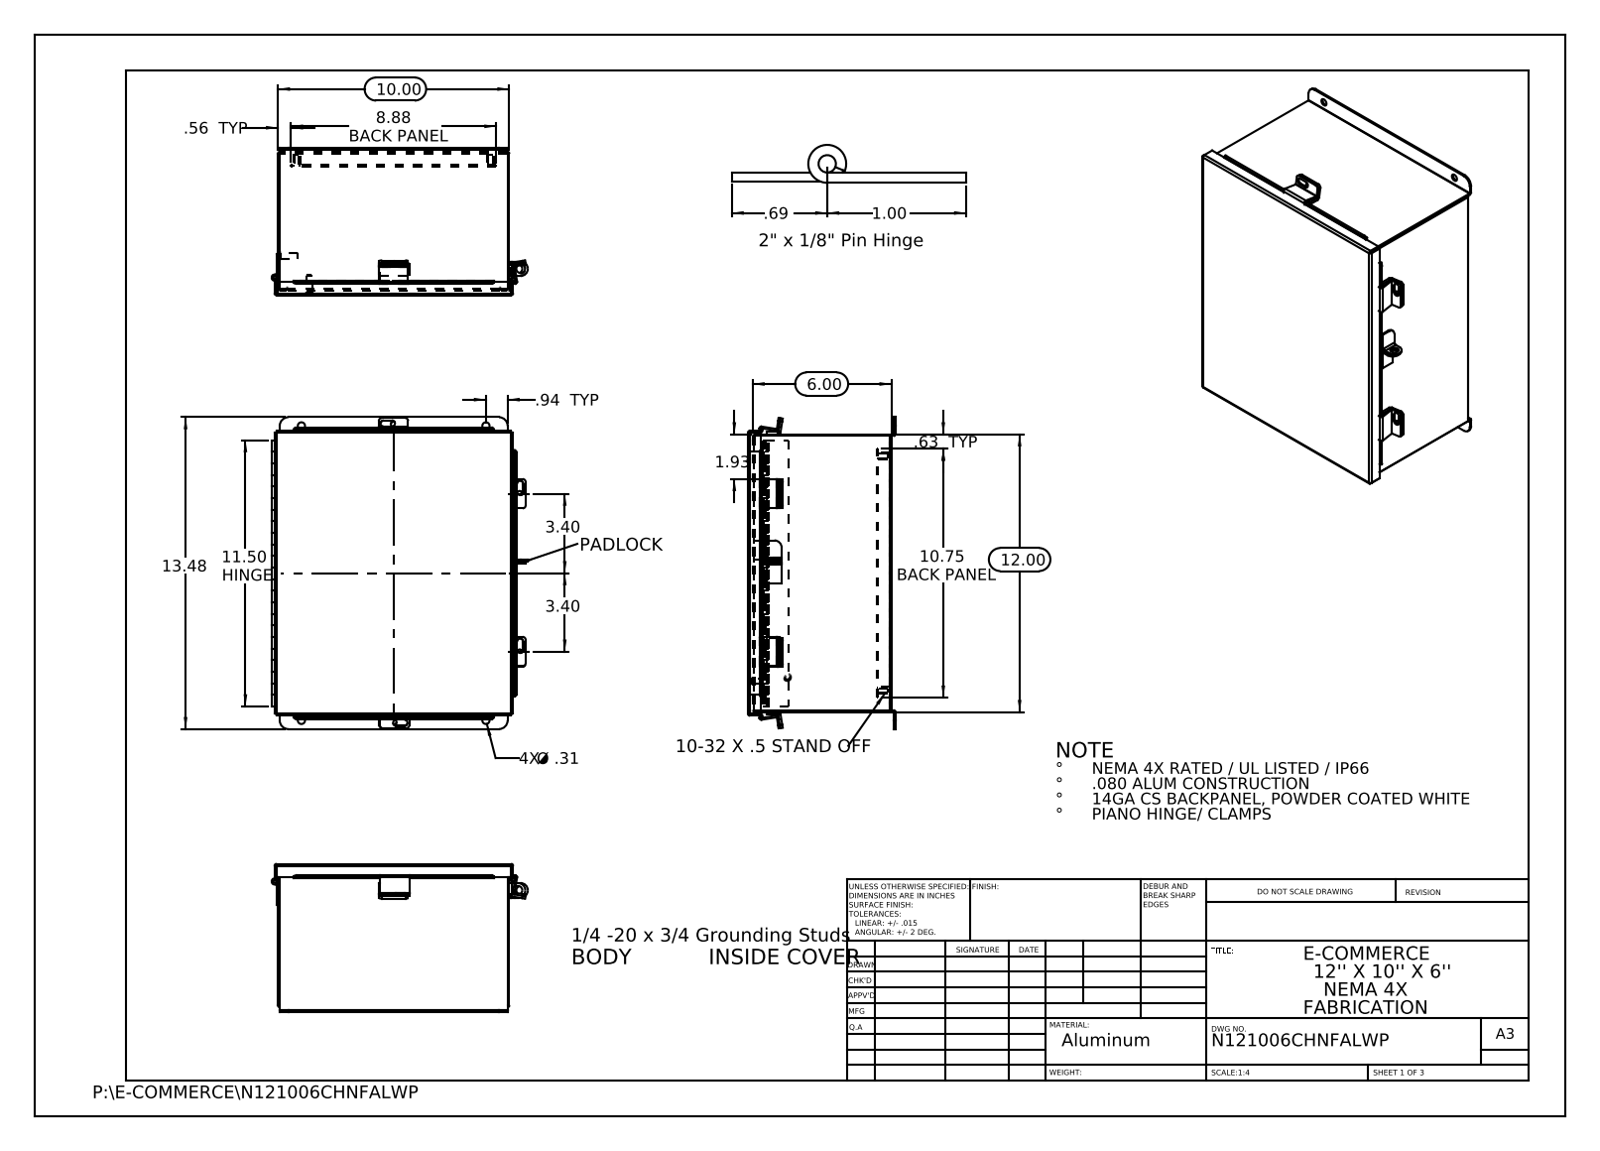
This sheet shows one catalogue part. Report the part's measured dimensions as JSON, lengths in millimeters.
{"part_name": "HW-CLH-JH-20104; N121006CHNFALWP JIC_Standoff; N121006CHNFALWP _JIC Hinge; N121006CHNFALWP JIC Enclosure Template (+8 more)", "step_written_by": "SolidWorks 2013 (CONFIG_CONTROL_DESIGN)", "units": "millimeters", "bodies": {"solids": 23, "faces": 702, "planar": 435, "cylindrical": 247, "other": 20}, "overall_size": [342.3, 281.2, 162.3], "volume_mm3": 848800, "surface_area_mm2": 912900, "round_holes": [[6.4, 8], [4.7, 4], [7.9, 4], [3.2, 1], [3.2, 1], [9.5, 1], [9.5, 1]], "round_bosses_or_shafts": [[8, 4], [8, 2], [6, 2], [6.9, 1], [6.4, 1]], "partial_cylinders_radius": [[3.2, 14], [0.3, 13], [0.2, 12], [2.2, 12], [3.4, 8], [2.1, 6], [2.5, 6], [9.5, 4]], "face_to_face_distances": [1.9, 155.7, 252.1, 302.9, 153.7, 157.6, 1.9, 14.6, 12.7, 141], "hole_center_spacings": [33.4, 210.3, 290.3, 356.9, 202.6, 212.7, 257.2, 323.2]}
